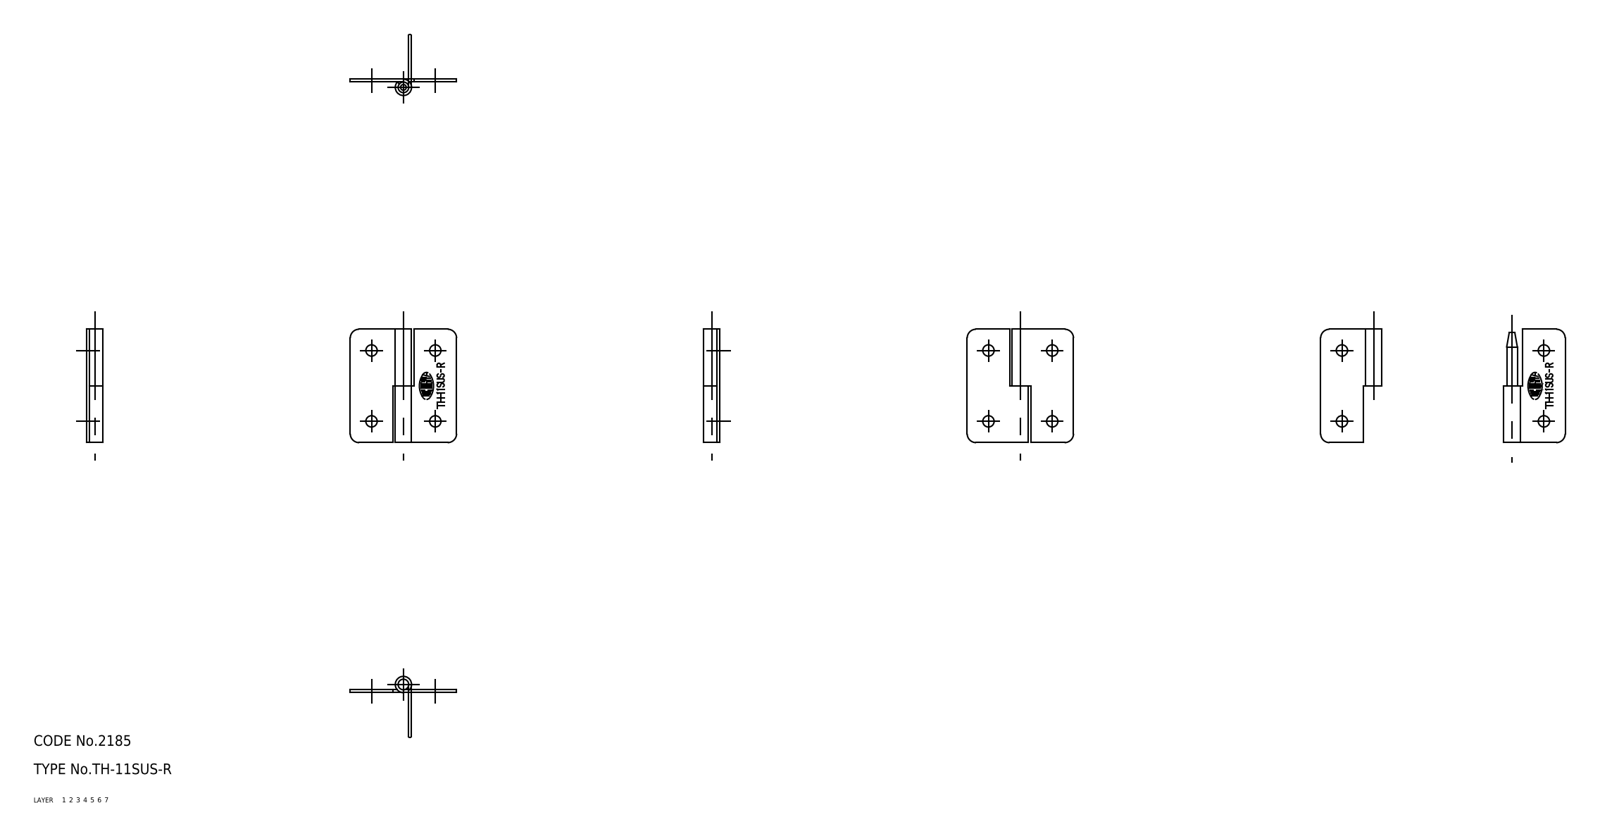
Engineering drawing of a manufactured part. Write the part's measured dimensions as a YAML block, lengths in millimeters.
part_name: "shaft; hinge piece_B_mr; hinge piece_A_mr; TH_11SUS_R_238_36"
step_written_by: "CADfix (AUTOMOTIVE_DESIGN)"
units: millimeters
bodies: {solids: 3, faces: 38, planar: 0, cylindrical: 0, other: 38}
overall_size: [32, 30, 4.6]
volume: 1133
surface_area: 2815
